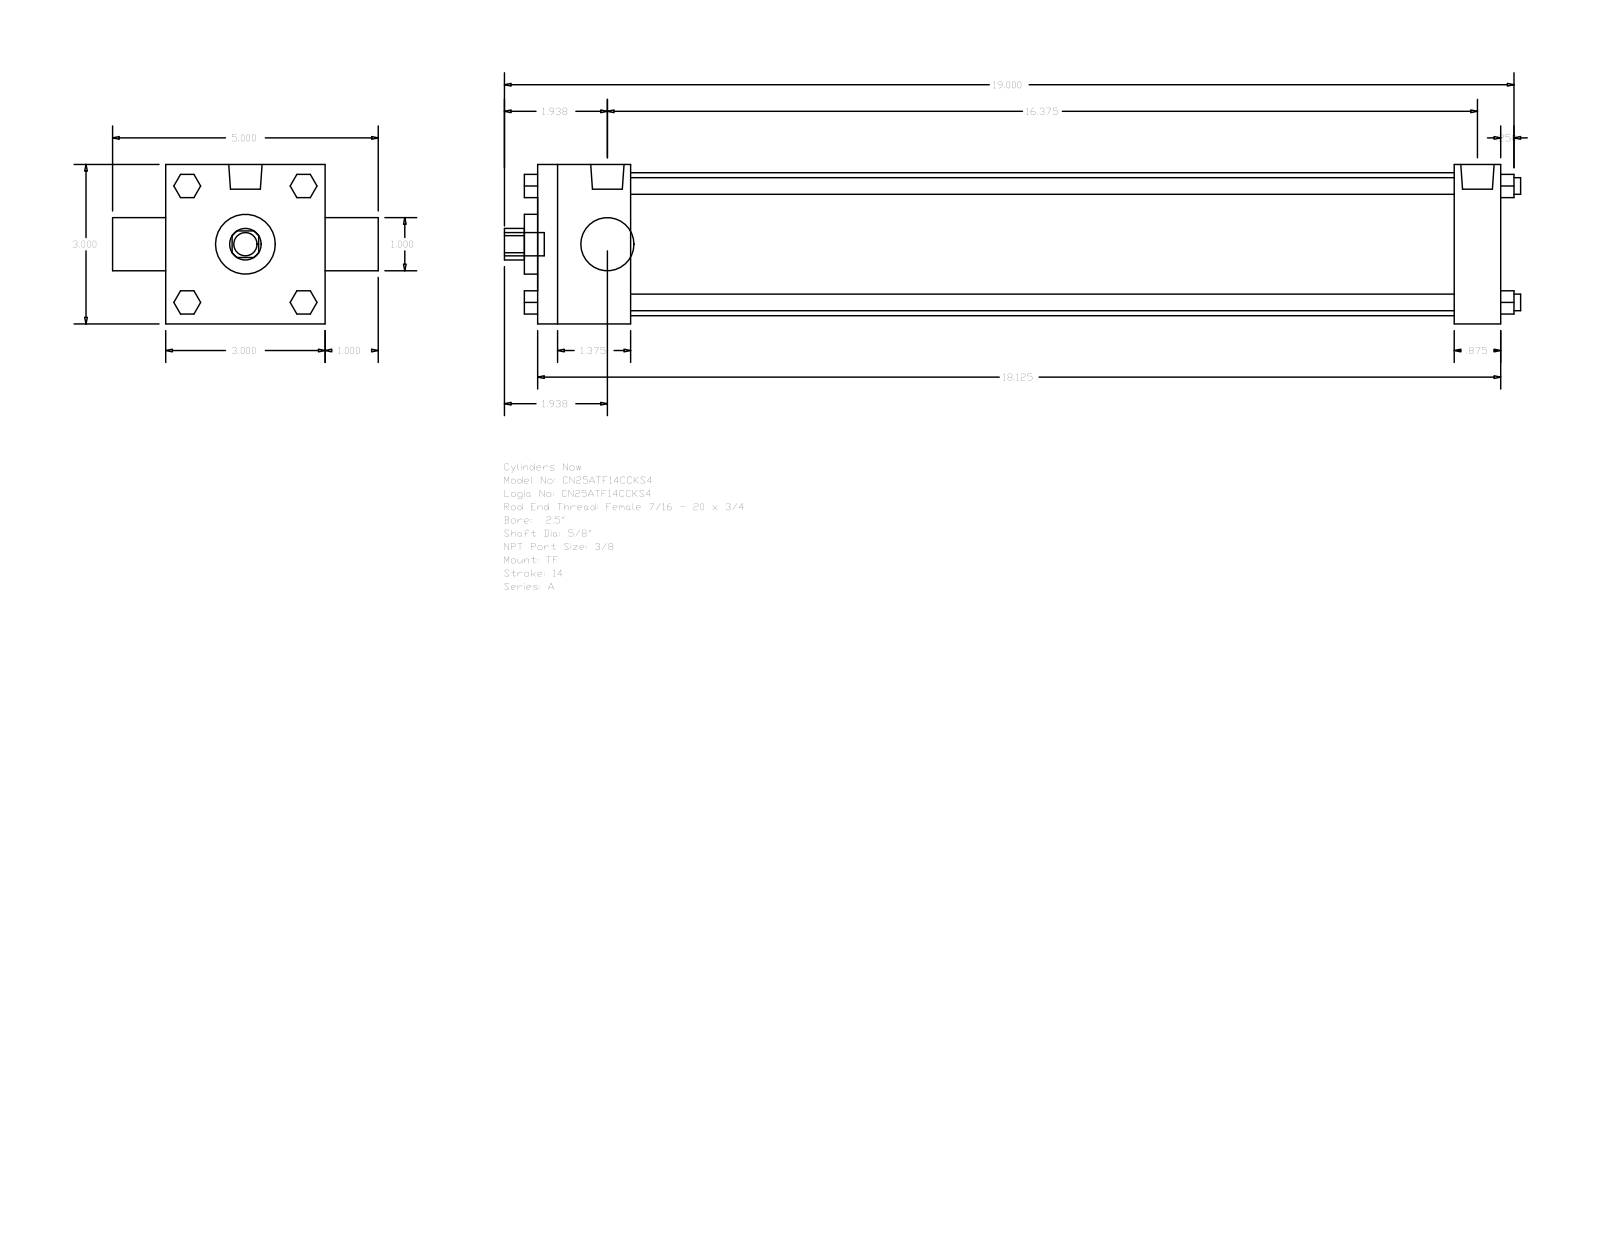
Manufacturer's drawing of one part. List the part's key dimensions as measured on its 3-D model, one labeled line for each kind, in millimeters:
Part name (STEP PRODUCT): A_TF__0250_0.625
STEP written by: GSSL Pune (CONFIG_CONTROL_DESIGN)
Units: millimetres
Bodies: 0 solids, 120 faces (92 planar, 28 cylindrical, 0 other)
Overall size (bounding box): 485.77 × 127 × 76.2
Round holes (diameter × count): ⌀15.88 ×1, ⌀25.4 ×1, ⌀28.57 ×1, ⌀68.33 ×1
Round bosses / shafts (diameter × count): ⌀7.94 ×4, ⌀5.56 ×3, ⌀15.93 ×2, ⌀11.11 ×1
Partial cylindrical surfaces — rounded edges, fillets, slot ends (radius × count): R7.54 ×1
Main face-to-face distances: 76.2, 460.37, 44.45, 438.14, 393.69, 415.92, 22.23, 25.4, 101.6, 466.72
